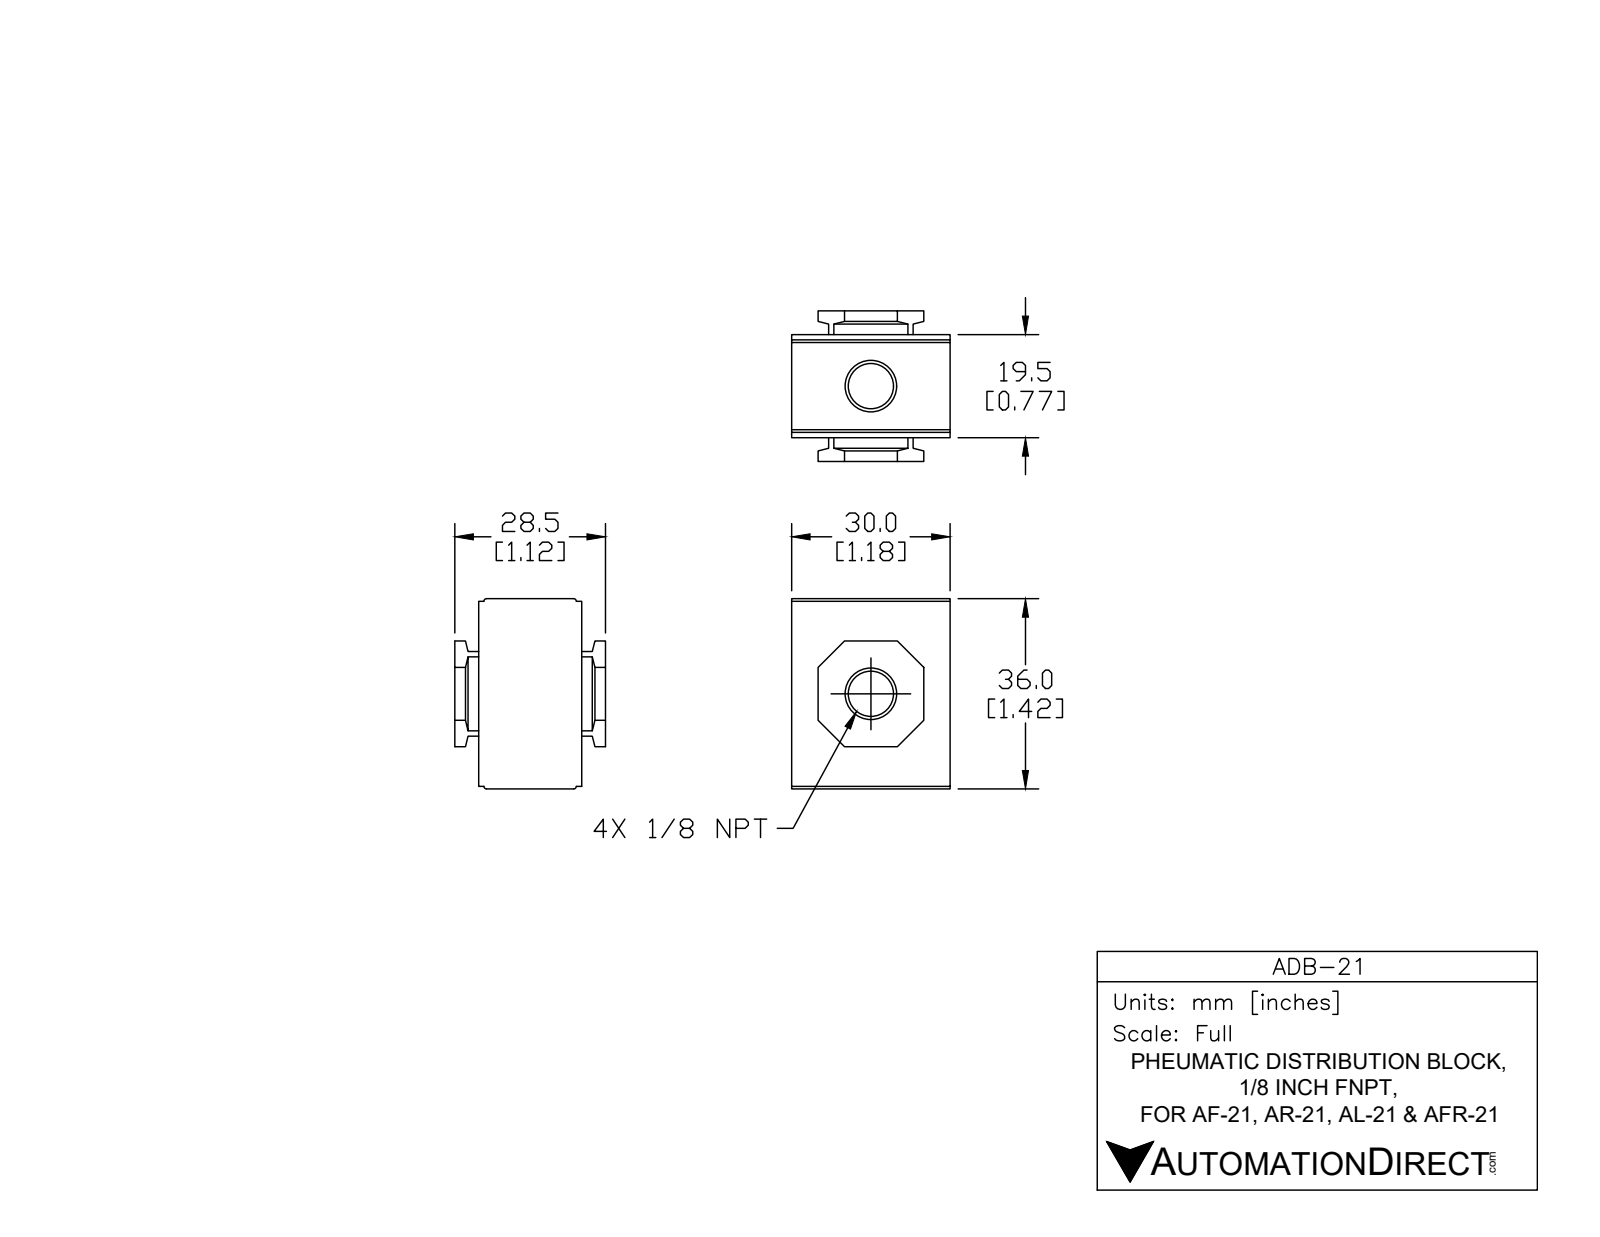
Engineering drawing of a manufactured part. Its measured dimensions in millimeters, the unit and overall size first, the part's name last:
Units: millimetres
Overall size (bounding box): 36 × 30 × 28.5
Round holes (diameter × count): ⌀8.6 ×2
Partial cylindrical surfaces — rounded edges, fillets, slot ends (radius × count): R0.5 ×4
Main face-to-face distances: 19.5, 30, 4.5, 24, 36, 28.5, 2, 18, 0.5, 35.5
Volume: 20 400 mm³ · Surface area: 6 806 mm²
Bodies: 1 solid, 64 faces (44 planar, 12 cylindrical, 8 other)
Part name (STEP PRODUCT): ADB-21
STEP written by: SolidWorks 2014 (AUTOMOTIVE_DESIGN)
